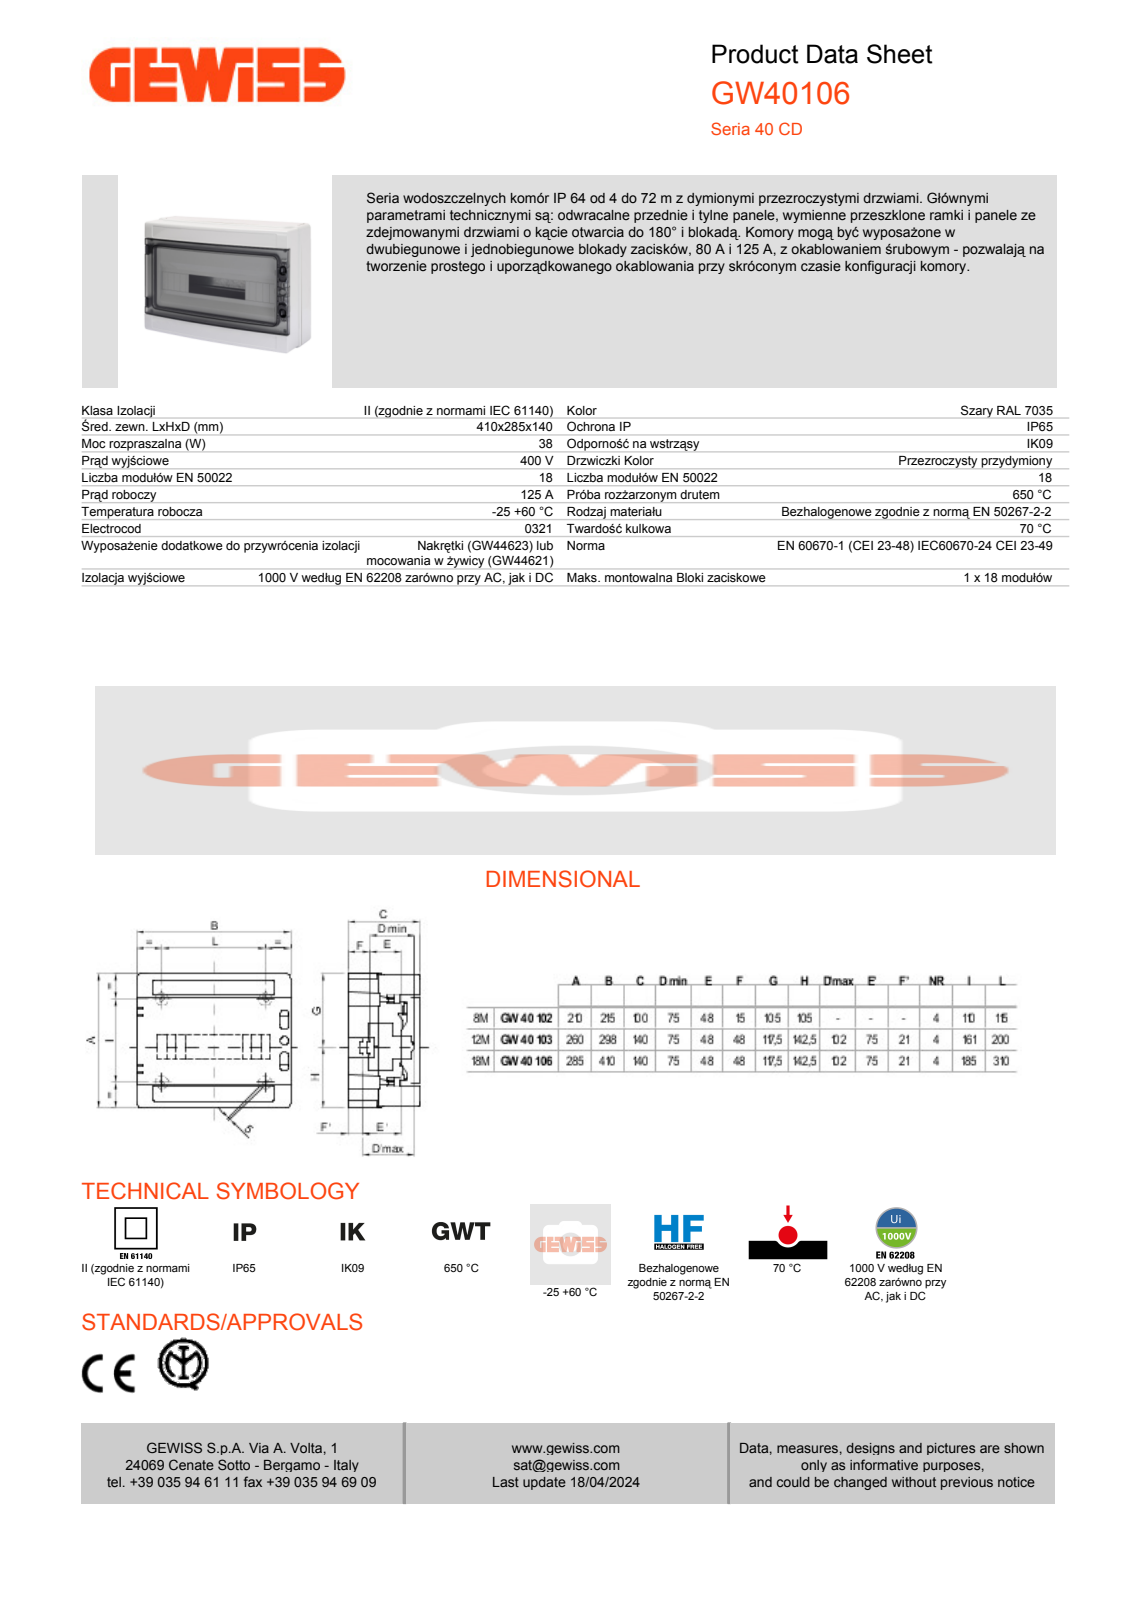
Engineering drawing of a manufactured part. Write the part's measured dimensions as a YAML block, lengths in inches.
part_name: "GW40106_COMPONENTE_B_OR; GW40106_COMPONENTE_A_OR; GUIDA_DIN_18_1; GW40106_ASM"
step_written_by: "CREO PARAMETRIC BY PTC INC, 2020354 (CONFIG_CONTROL_DESIGN)"
units: inches
bodies: {solids: 3, faces: 931, planar: 549, cylindrical: 210, other: 172}
overall_size: [16.142, 11.22, 5.63]
volume: 235.3
surface_area: 1493
round_holes:
  - {diameter: 0.126, count: 4}
  - {diameter: 0.433, count: 4}
  - {diameter: 0.827, count: 4}
  - {diameter: 0.165, count: 1}
  - {diameter: 1.52, count: 1}
round_bosses_or_shafts:
  - {diameter: 0.984, count: 4}
  - {diameter: 1.757, count: 1}
partial_cylinders:
  - {radius: 0.118, count: 8}
  - {radius: 0.157, count: 6}
  - {radius: 0.276, count: 6}
  - {radius: 0.374, count: 6}
  - {radius: 0.031, count: 4}
  - {radius: 0.071, count: 4}
  - {radius: 0.083, count: 4}
  - {radius: 0.201, count: 4}
face_to_face_distances: [0.118, 0.157, 0.246, 0.128, 0.089, 0.03, 11.063, 10.974, 10.817, 4.331]
hole_center_spacings: [1.299, 7.106, 7.283, 7.398, 8.249, 13.504, 15.343, 0.693]
